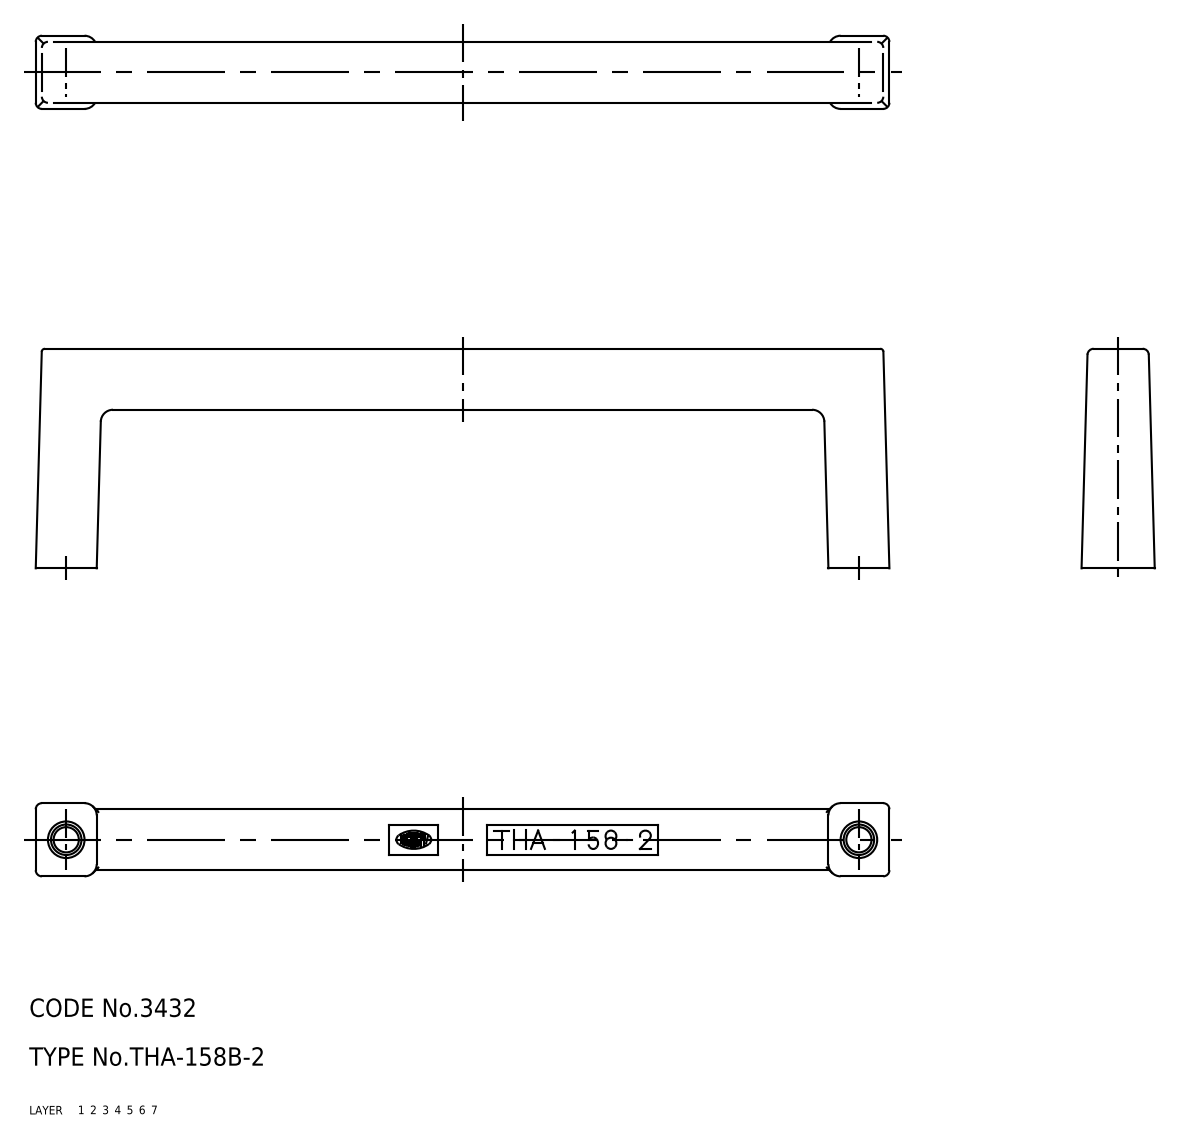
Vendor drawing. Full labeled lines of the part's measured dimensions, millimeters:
Part name (STEP PRODUCT): 67111149
STEP written by: CADfix (AUTOMOTIVE_DESIGN)
Units: millimetres
Bodies: 1 solid, 44 faces (0 planar, 0 cylindrical, 44 other)
Overall size (bounding box): 140 × 36 × 12
Volume: 19 221 mm³ · Surface area: 7 925 mm²
